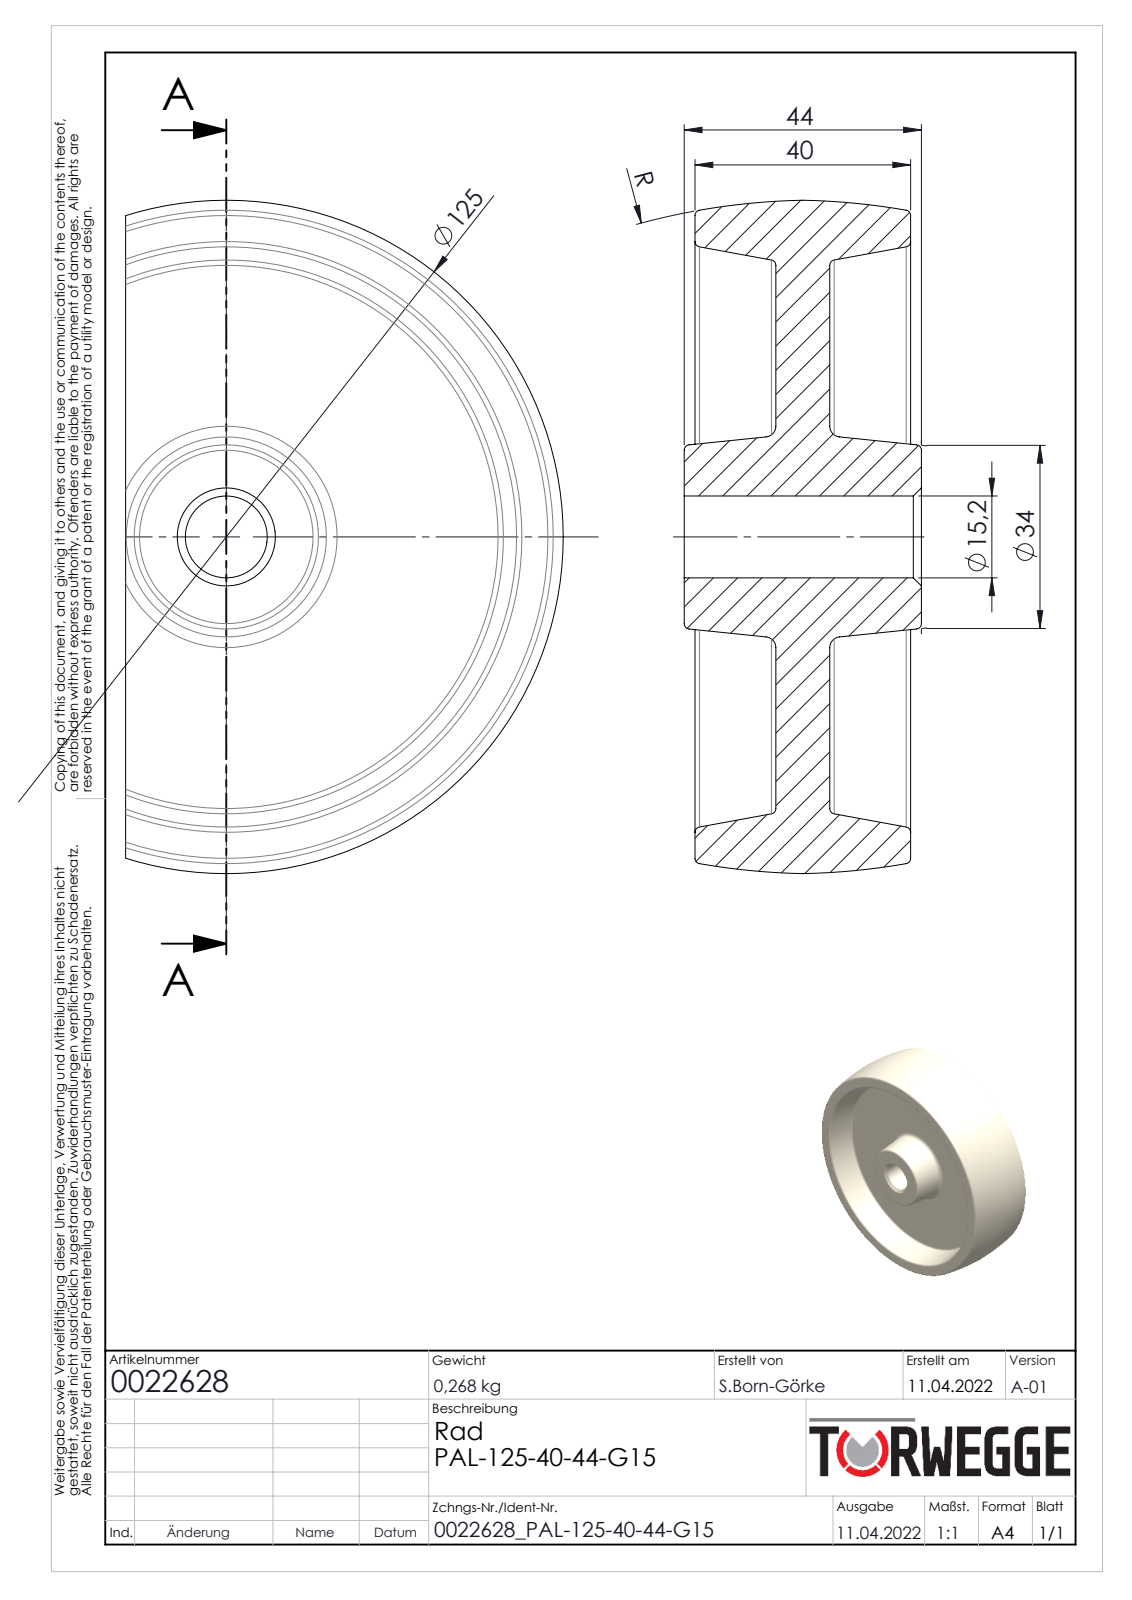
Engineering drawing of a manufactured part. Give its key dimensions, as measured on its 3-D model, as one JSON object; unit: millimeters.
{"part_name": "0022628", "step_written_by": "SolidWorks 2020 (AUTOMOTIVE_DESIGN)", "units": "millimeters", "bodies": {"solids": 1, "faces": 42, "planar": 6, "cylindrical": 2, "other": 34}, "overall_size": [125, 125, 44], "volume_mm3": 244597, "surface_area_mm2": 51219, "round_holes": [[15.2, 1]], "face_to_face_distances": [10, 15, 25, 40, 2, 17, 27, 42, 44]}
